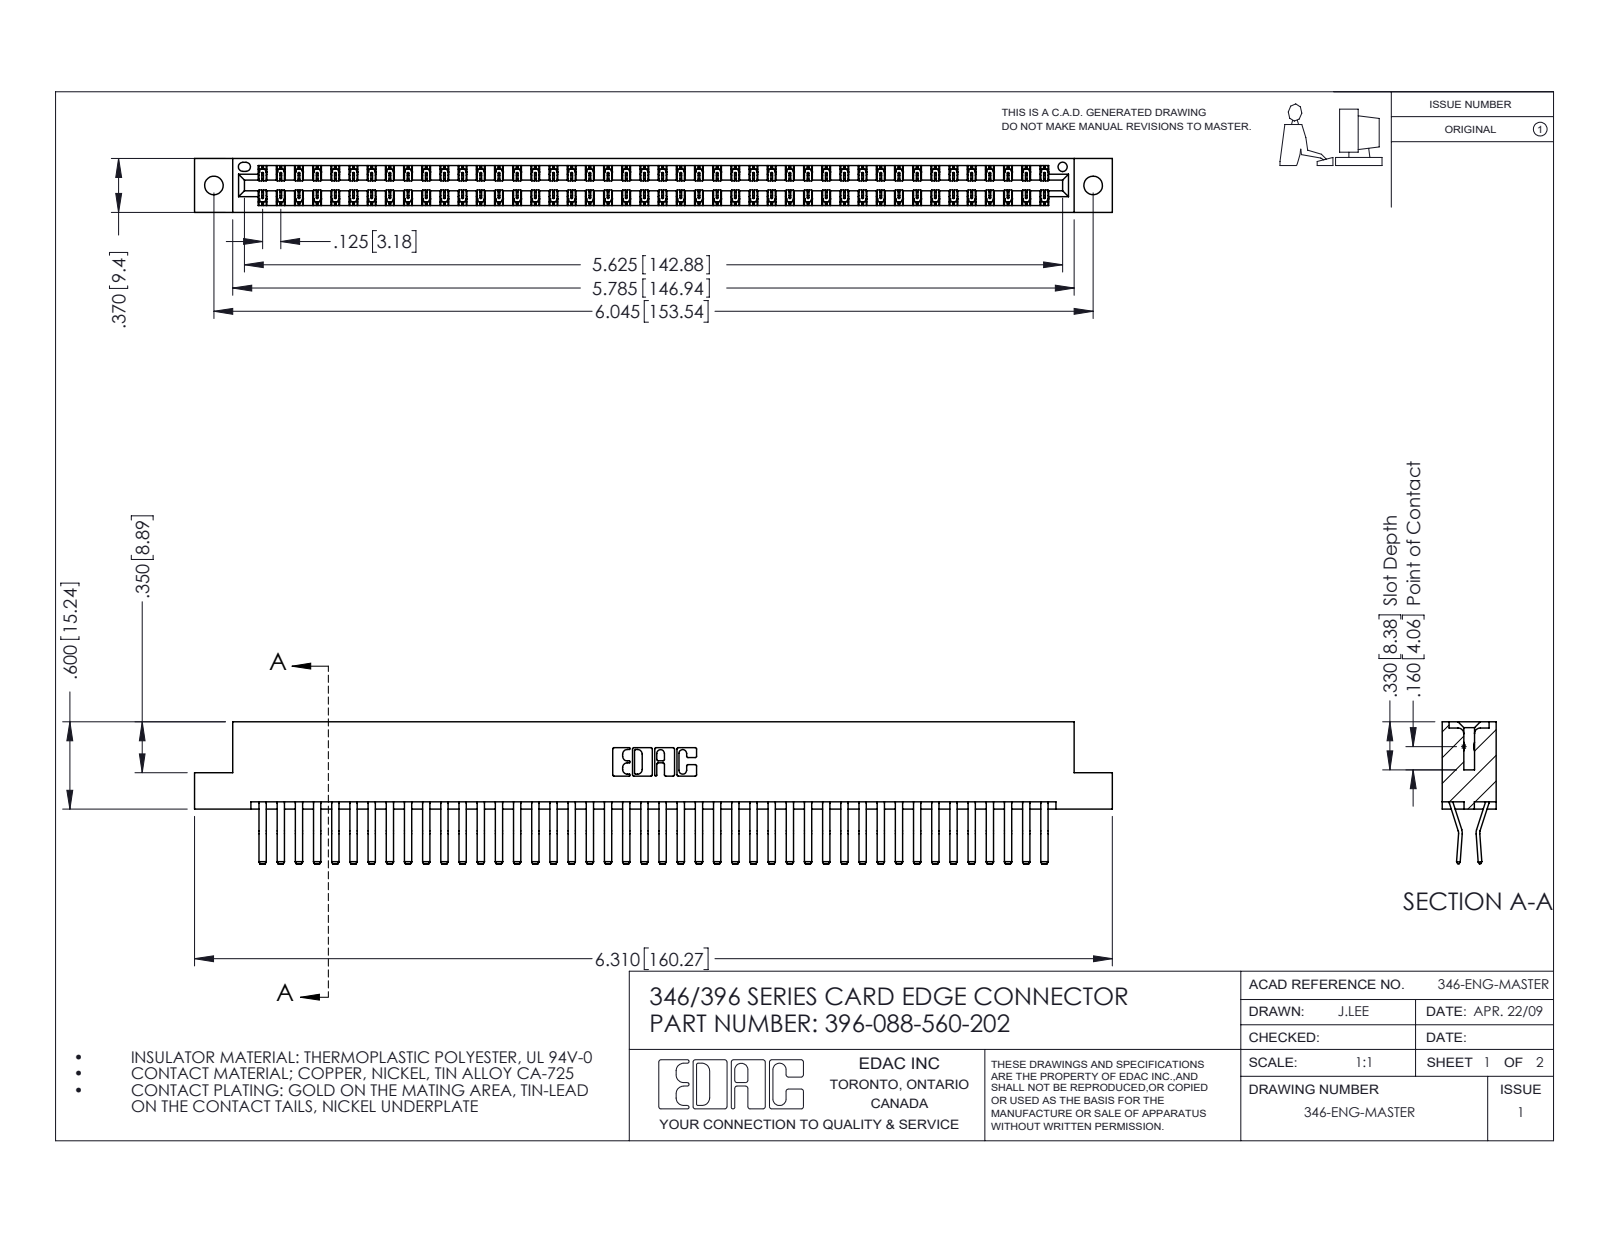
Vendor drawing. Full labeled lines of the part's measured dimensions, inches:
Part name (STEP PRODUCT): 396-088-560-202; 346 Part_Flush Mounting Lugs - 0.128 Dia; 345-292-001_560 Tail
STEP written by: SolidWorks 2016 (CONFIG_CONTROL_DESIGN)
Units: inches
Bodies: 89 solids, 4874 faces (3156 planar, 1718 cylindrical, 0 other)
Overall size (bounding box): 6.31 × 0.975 × 0.37
Volume: 0.988 in³ · Surface area: 36.5 in²
Round holes (diameter × count): ⌀0.128 ×2, ⌀0.064 ×1
Partial cylindrical surfaces — rounded edges, fillets, slot ends (radius × count): R0.006 ×132, R0.01 ×22, R0.007 ×6, R0.031 ×6, R0.026 ×3, R0.01 ×2, R0.014 ×2, R0.022 ×2
Main face-to-face distances: 0.048, 0.322, 0.37, 0.025, 0.25, 0.072, 0.298, 0.275, 0.148, 0.222
Hole centre spacings: 0.246, 5.836, 6.045
